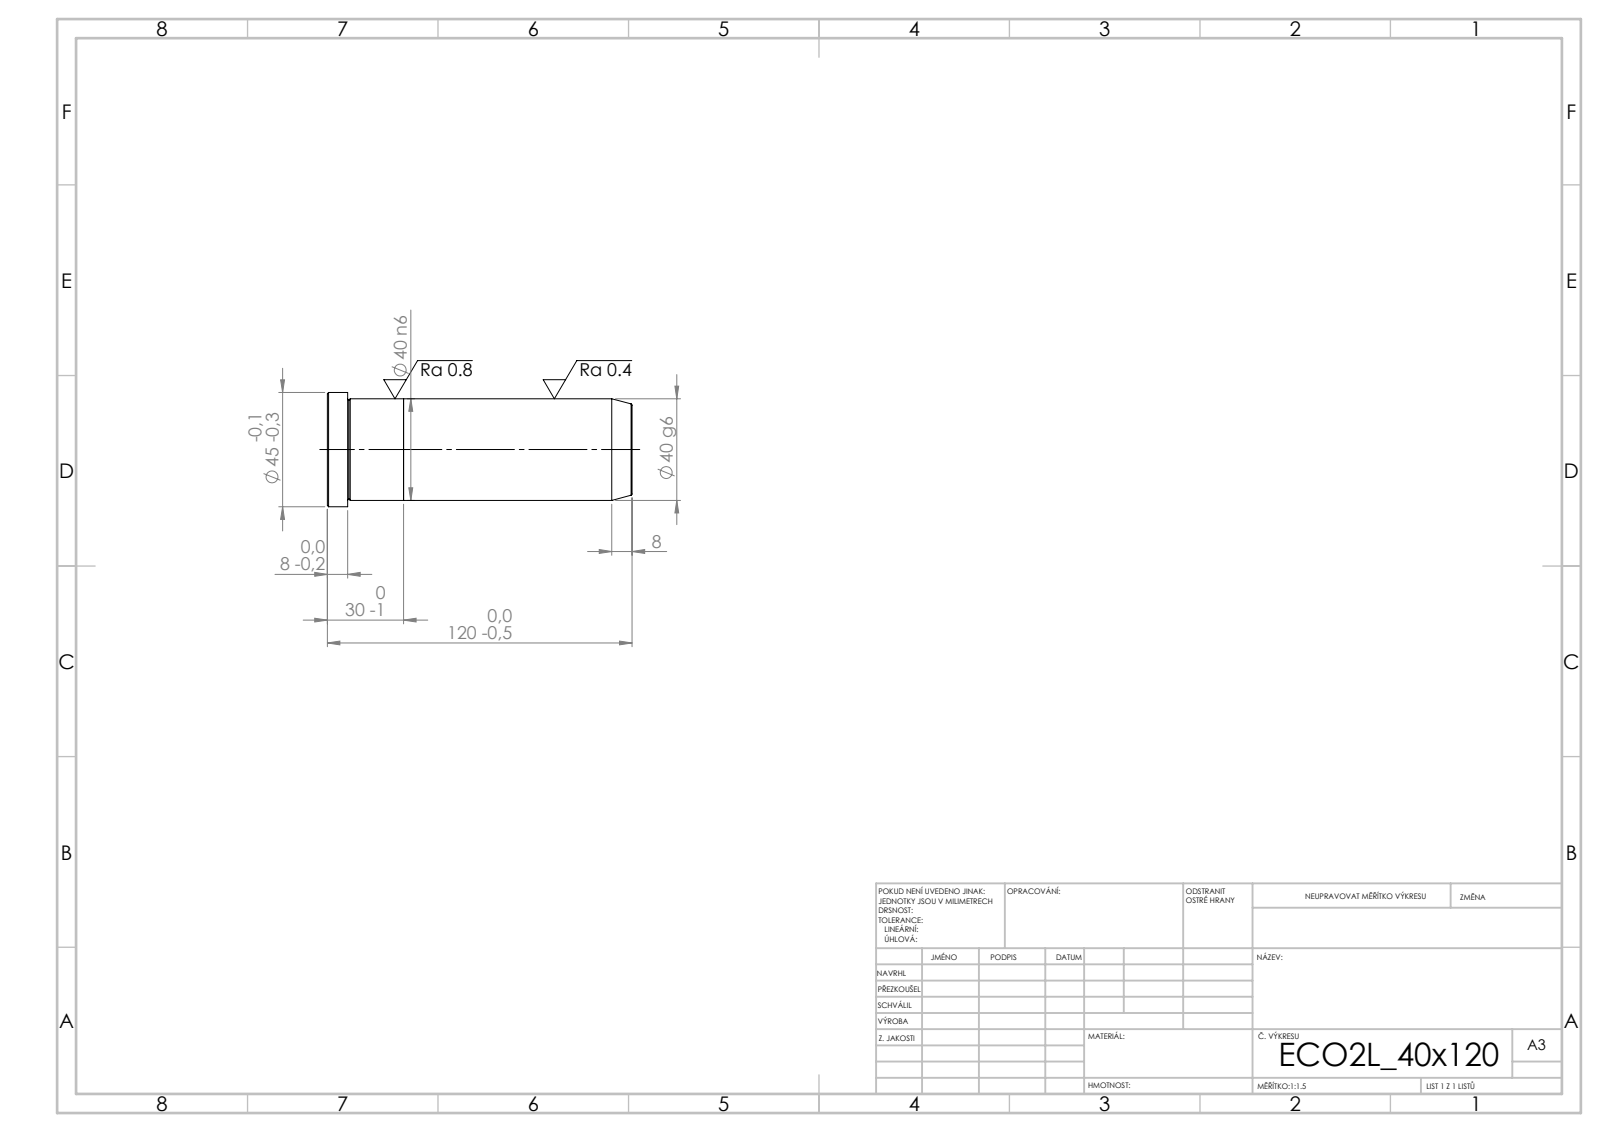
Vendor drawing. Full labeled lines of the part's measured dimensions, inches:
STEP written by: SolidWorks 2019 (CONFIG_CONTROL_DESIGN)
Units: inches
Bodies: 2 solids, 21 faces (5 planar, 6 cylindrical, 10 other)
Overall size (bounding box): 4.724 × 1.772 × 1.772
Volume: 9.297 in³ · Surface area: 31.99 in²
Round bosses / shafts (diameter × count): ⌀1.772 ×1, ⌀1.575 ×1
Main face-to-face distances: 1.181, 3.543, 4.724, 4.409, 0.866, 0.315
